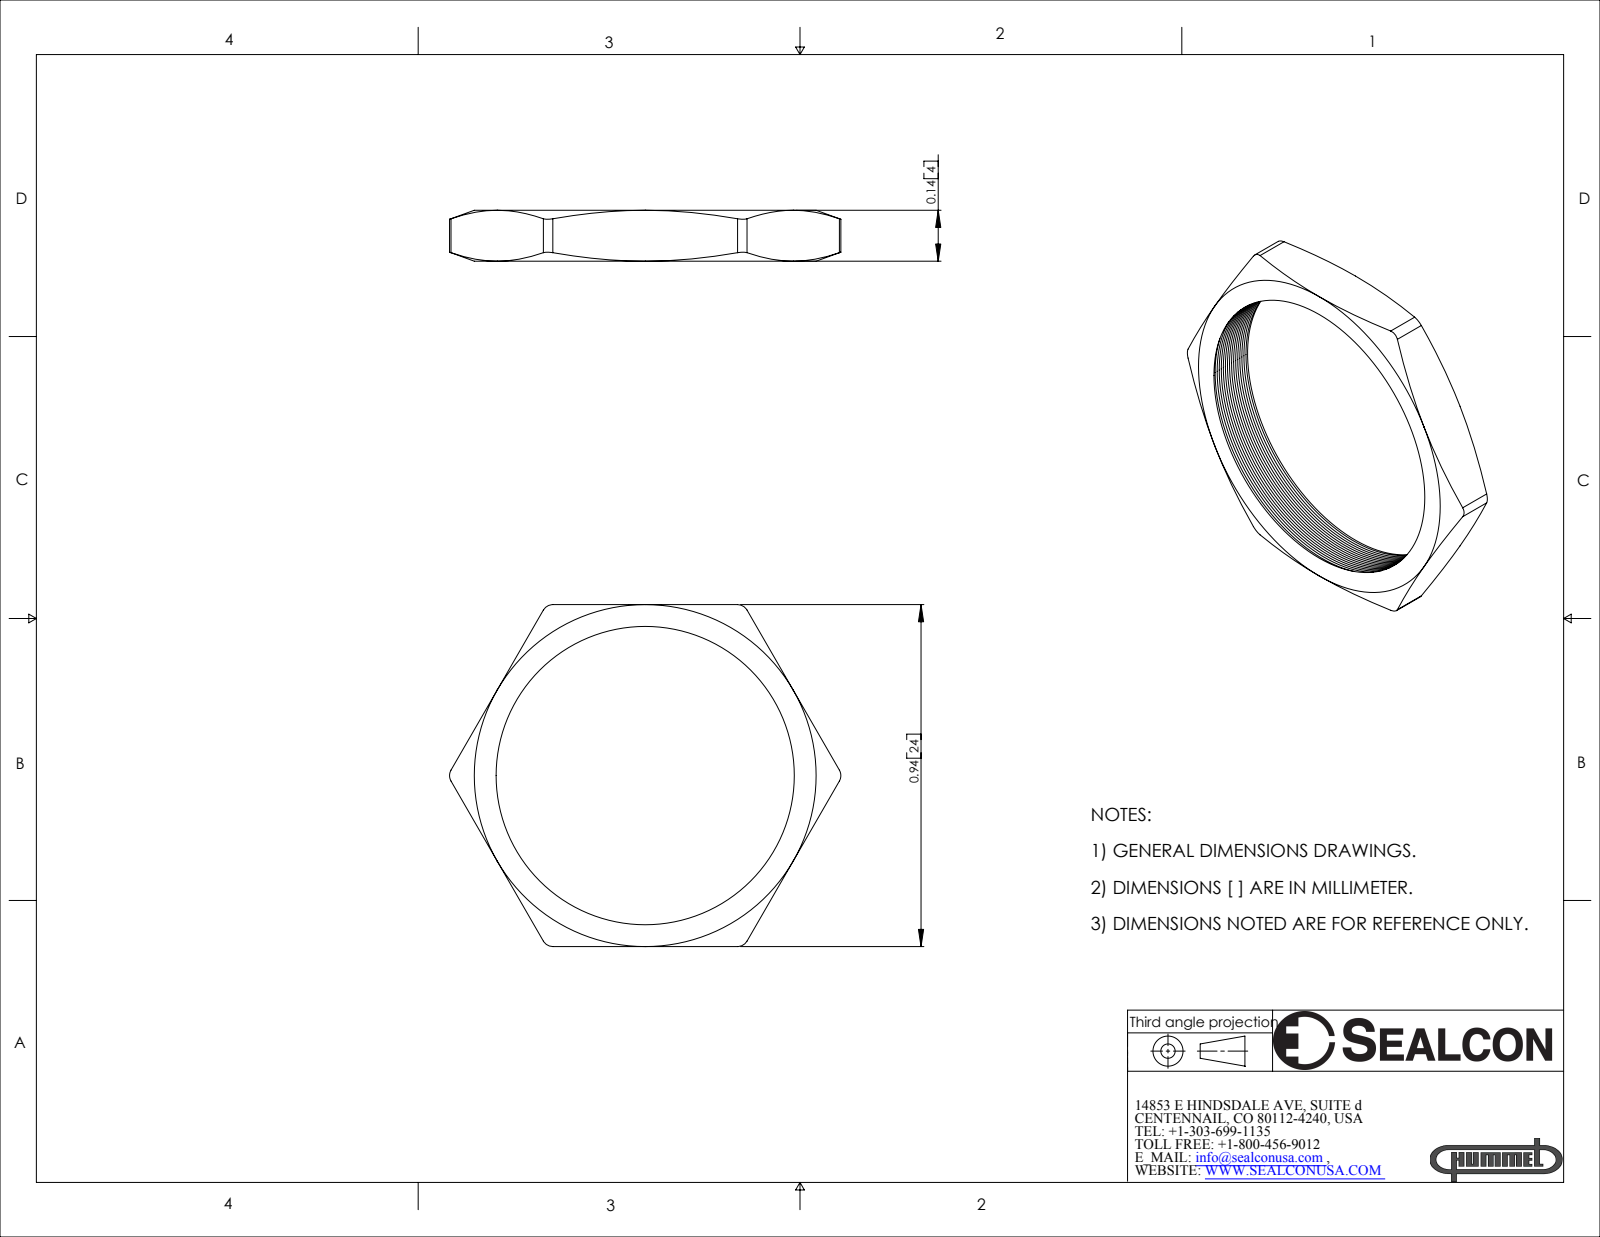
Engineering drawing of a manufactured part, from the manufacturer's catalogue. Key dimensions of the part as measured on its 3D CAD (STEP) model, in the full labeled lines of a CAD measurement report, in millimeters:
Part name (STEP PRODUCT): NN-13-BR
STEP written by: SolidWorks 2007 (CONFIG_CONTROL_DESIGN)
Units: millimetres
Bodies: 1 solid, 97 faces (8 planar, 7 cylindrical, 82 other)
Overall size (bounding box): 27.3 × 23.9 × 3.6
Volume: 460 mm³ · Surface area: 1 029 mm²
Partial cylindrical surfaces — rounded edges, fillets, slot ends (radius × count): R0.8 ×6
Main face-to-face distances: 23.9, 3.6
